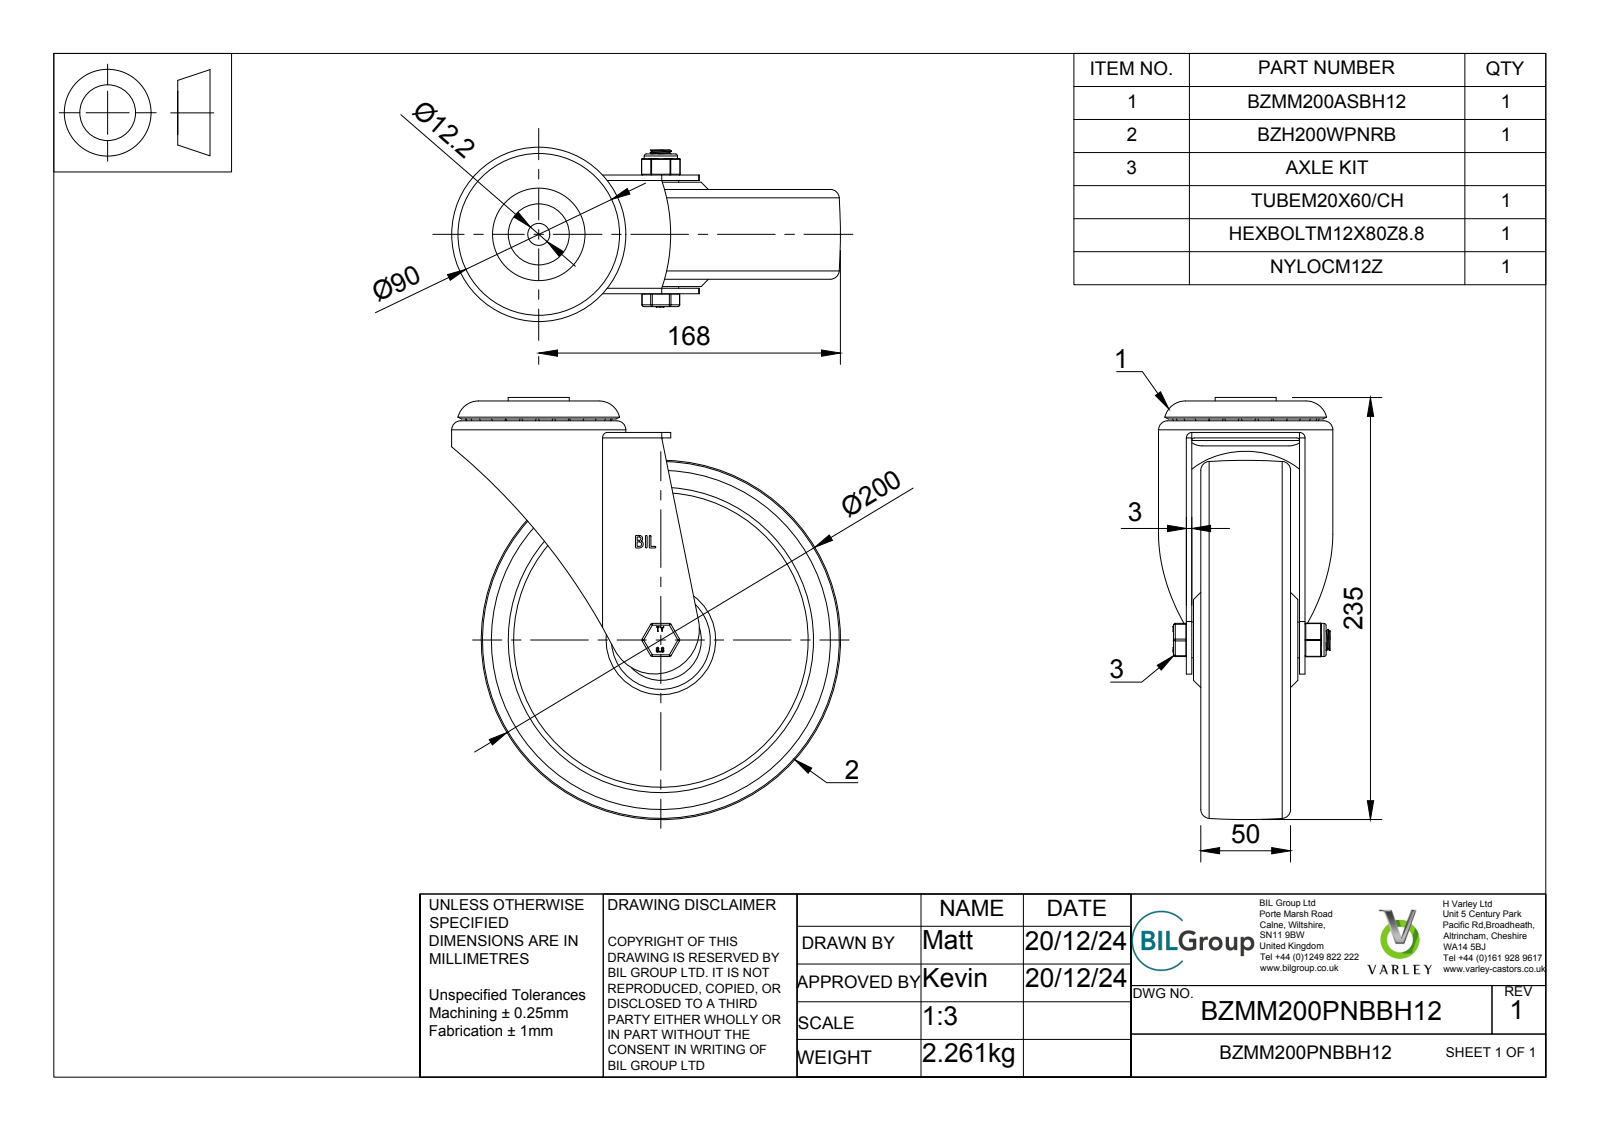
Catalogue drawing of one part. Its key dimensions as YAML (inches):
part_name: "BZMM200PNBBH12 v3; BZMM200ASBH12 v1; ZINC PLATED, PRESSED STEEL HEAD; ZINC PLATED, PRESSED STEEL HEAD Geometry (+6 more)"
step_written_by: "Autodesk Translation Framework v13.20.0.188 (AP242_MANAGED_MODEL_BASED_3D_ENGINEERING_MIM_LF)"
units: inches
bodies: {solids: 65, faces: 493, planar: 198, cylindrical: 155, other: 140}
overall_size: [9.252, 8.524, 3.819]
volume: 56.89
surface_area: 466.3
round_holes:
  - {diameter: 0.472, count: 1}
  - {diameter: 0.48, count: 1}
  - {diameter: 0.484, count: 1}
  - {diameter: 0.492, count: 1}
  - {diameter: 0.551, count: 1}
  - {diameter: 0.787, count: 1}
  - {diameter: 0.807, count: 1}
  - {diameter: 1.181, count: 1}
  - {diameter: 1.26, count: 1}
  - {diameter: 2.008, count: 1}
  - {diameter: 2.283, count: 1}
  - {diameter: 3.583, count: 1}
round_bosses_or_shafts:
  - {diameter: 0.197, count: 10}
  - {diameter: 3.819, count: 1}
  - {diameter: 2.48, count: 1}
  - {diameter: 2.165, count: 1}
  - {diameter: 1.535, count: 1}
  - {diameter: 1.339, count: 1}
  - {diameter: 1.161, count: 1}
  - {diameter: 0.945, count: 1}
partial_cylinders:
  - {radius: 0.02, count: 18}
  - {radius: 0.039, count: 12}
  - {radius: 0.059, count: 4}
  - {radius: 0.118, count: 2}
  - {radius: 0.492, count: 1}
  - {radius: 0.984, count: 1}
  - {radius: 3.642, count: 1}
  - {radius: 14.122, count: 1}
face_to_face_distances: [0.433, 0.157, 0.315, 0.118, 0.197, 2.283, 0.768, 2.165, 2.126, 1.083]
